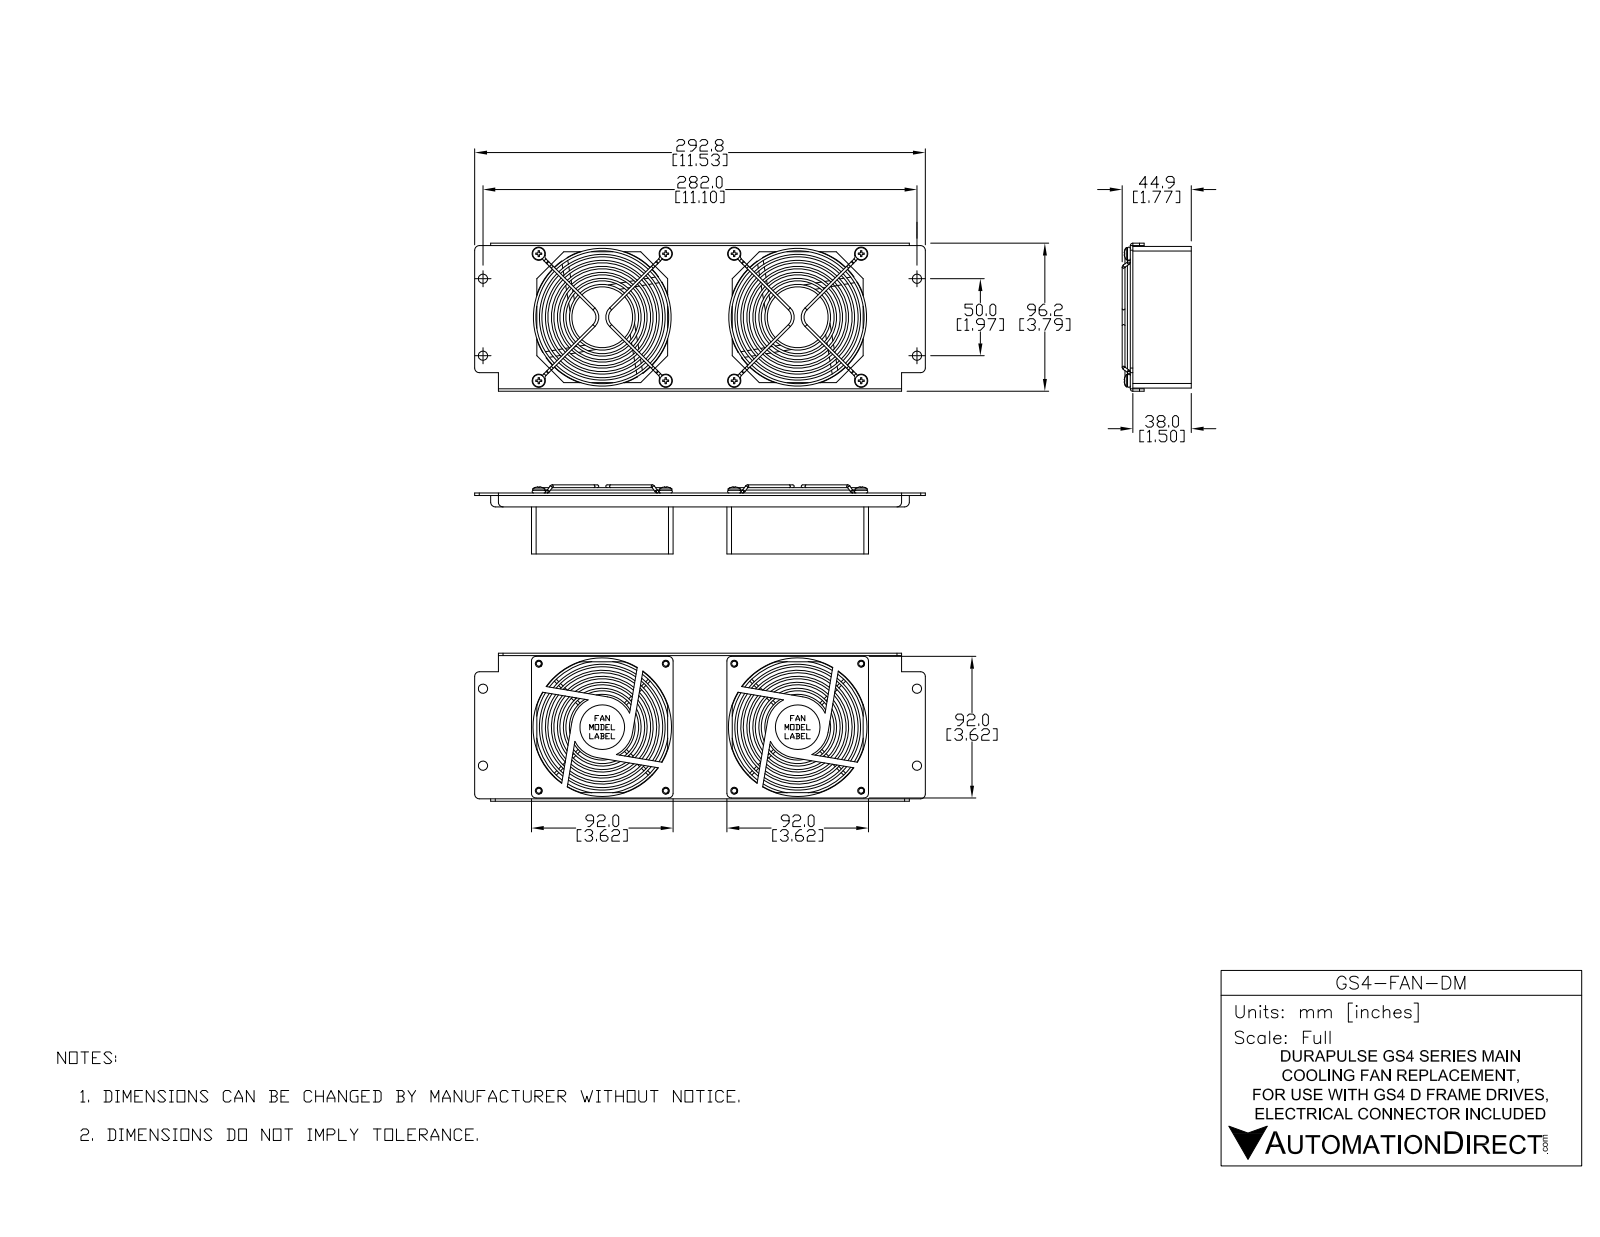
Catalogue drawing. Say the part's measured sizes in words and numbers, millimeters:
The part is named "GS4-FAN-DM-3D A Bolt; GS4-FAN-DM-3D A grill; GS4-FAN-DM-3D A flat flange only; GS4-FAN-DM-3D A Fan block only (+1 more)". Its 3-D file was written by "SolidWorks 2016 (AUTOMOTIVE_DESIGN)". It is 41 solids with 615 faces: 218 planar, 133 cylindrical and 264 other. Overall it measures 292.8 by 96.2 by 44.9 millimeters. Its volume is 328 100 cubic millimeters and its surface area 153 300 square millimeters. Round holes: 8 of diameter 4.5, 8 of diameter 4.5, 4 of diameter 6, 2 of diameter 90. Round bosses or shafts: 8 of diameter 7.9. Partial cylindrical surfaces (rounded edges, fillets, slot ends): 16 of radius 3, 2 of radius 1.6, 2 of radius 20. The main face-to-face distances are 1.6, 92, 4, 36, 38, 39.6, 127, 125.2, 40, 32. The hole center spacings are 82.5, 58.3, 116.7, 127, 151.4, 176.2, 39.7, 75.5.
